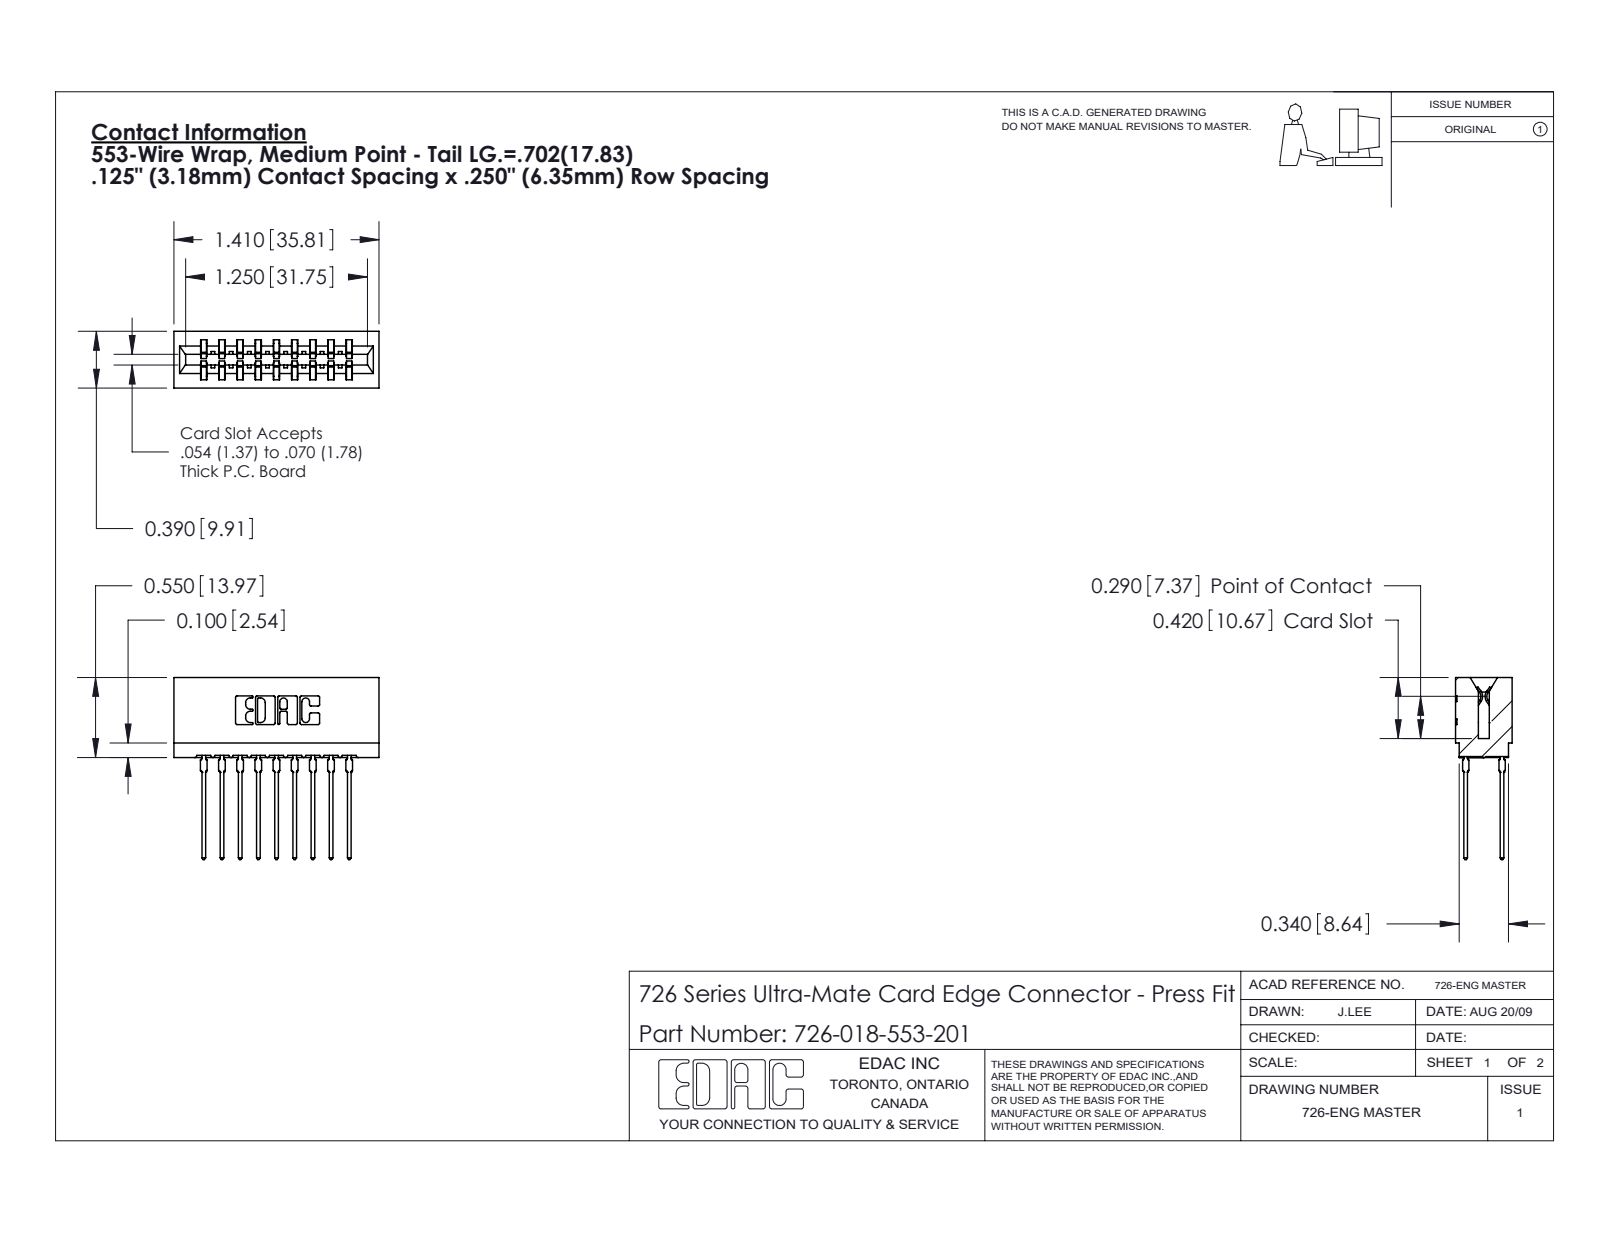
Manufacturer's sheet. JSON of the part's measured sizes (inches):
{"part_name": "746-292-001_553; 726-018-553-201; 726 Part_.515 Slot Depth - 01", "step_written_by": "SolidWorks 2020 (CONFIG_CONTROL_DESIGN)", "units": "inches", "bodies": {"solids": 19, "faces": 1708, "planar": 883, "cylindrical": 357, "other": 468}, "overall_size": [1.41, 1.251, 0.39], "volume_in3": 0.217, "surface_area_in2": 8.83, "partial_cylinders_radius": [[0.021, 36], [0.01, 22], [0.015, 10], [0.005, 8], [0.011, 8], [0.007, 6], [0.031, 6], [0.026, 3]], "face_to_face_distances": [0.25, 0.333, 0.057, 0.5, 0.042, 0.083, 0.125, 0.125, 0.025, 0.307]}
